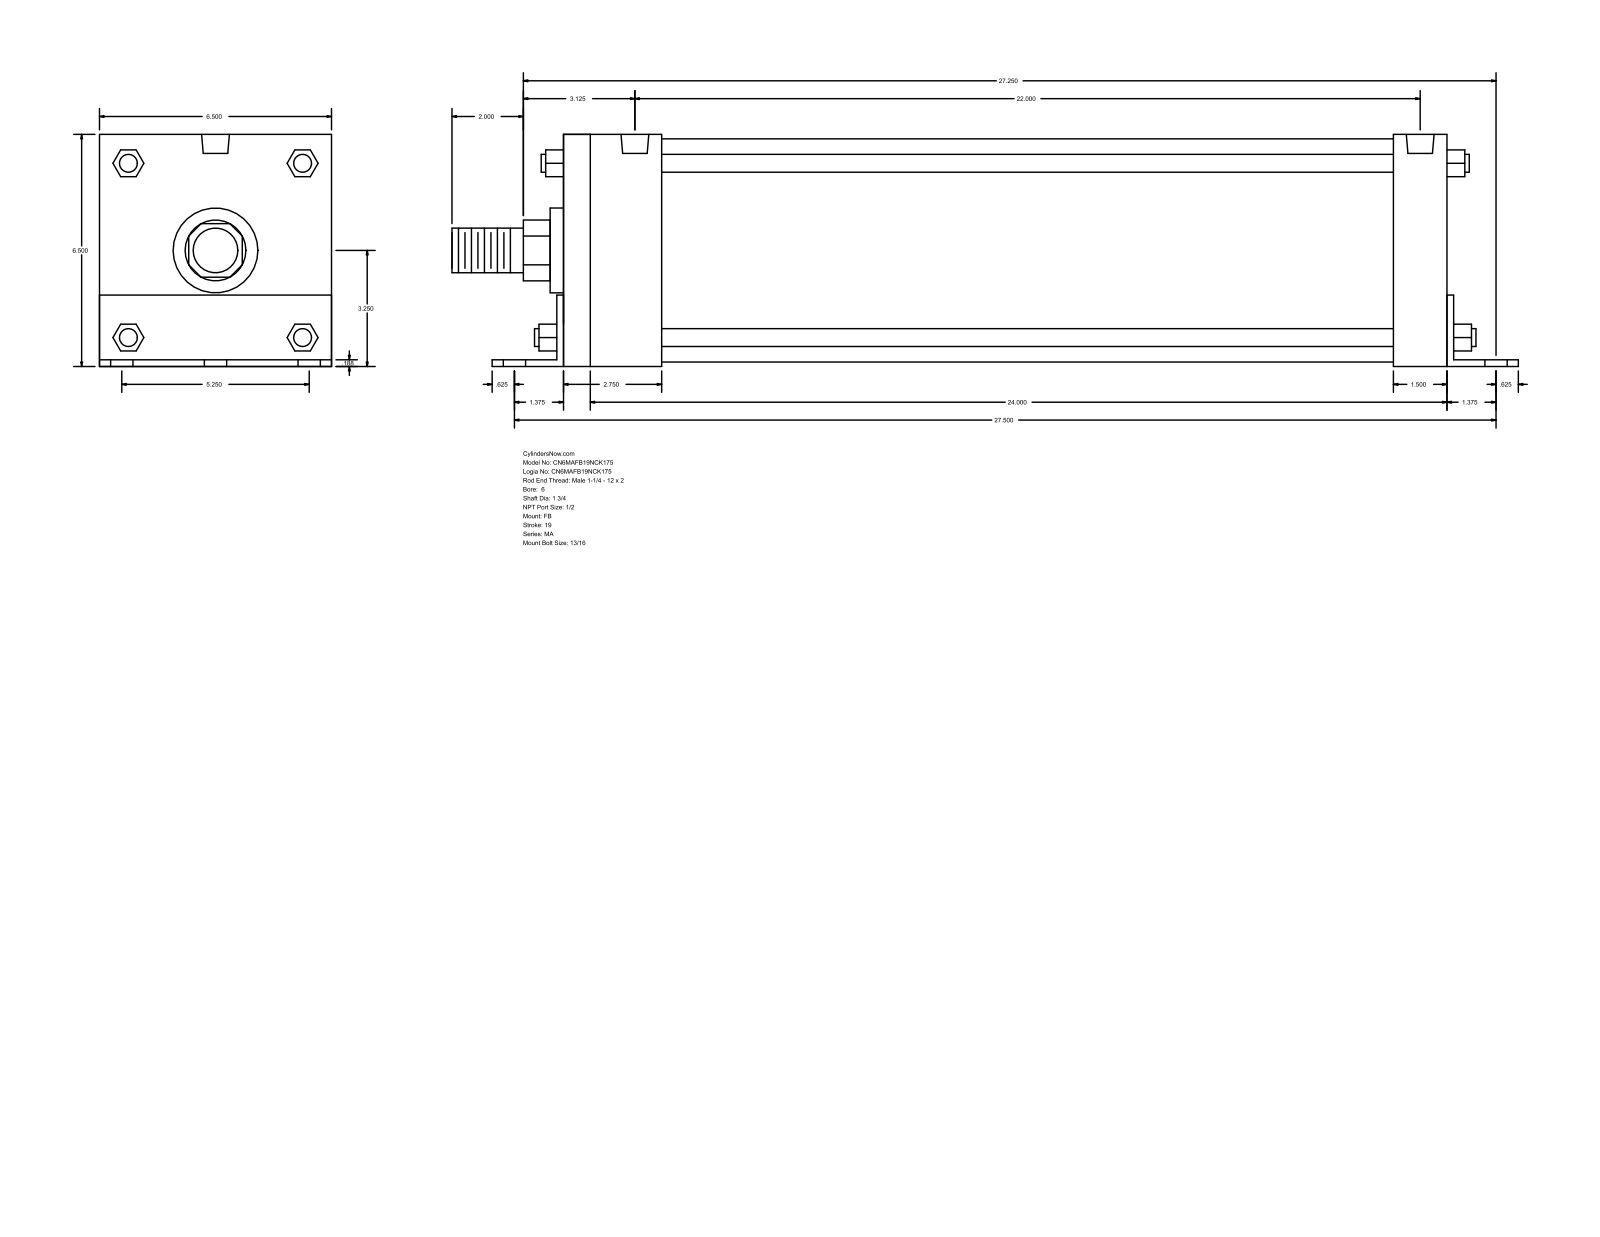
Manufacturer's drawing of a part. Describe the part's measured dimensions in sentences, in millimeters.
The part is named "MA_FB__0600_1.75". Its 3-D file was written by "GSSL Pune (CONFIG_CONTROL_DESIGN)". It is 0 solids with 140 faces: 105 planar, 35 cylindrical and 0 other. Overall it measures 758.83 by 165.15 by 165.1 millimeters. Round holes: 6 of diameter 20.64, 4 of diameter 17.46, 2 of diameter 19.77. Round bosses or shafts: 4 of diameter 12.7, 1 of diameter 158.75, 1 of diameter 60.33, 1 of diameter 44.45, 1 of diameter 31.75. Partial cylindrical surfaces (rounded edges, fillets, slot ends): 1 of radius 21.63, 1 of radius 32.05. The main face-to-face distances are 165.1, 4.76, 628.66, 165.15, 633.42, 4.71, 160.39, 638.18, 69.85, 74.61. The hole center spacings are 66.67, 701.67, 698.5, 85.78, 108.6, 133.34, 558.79, 616.39.
